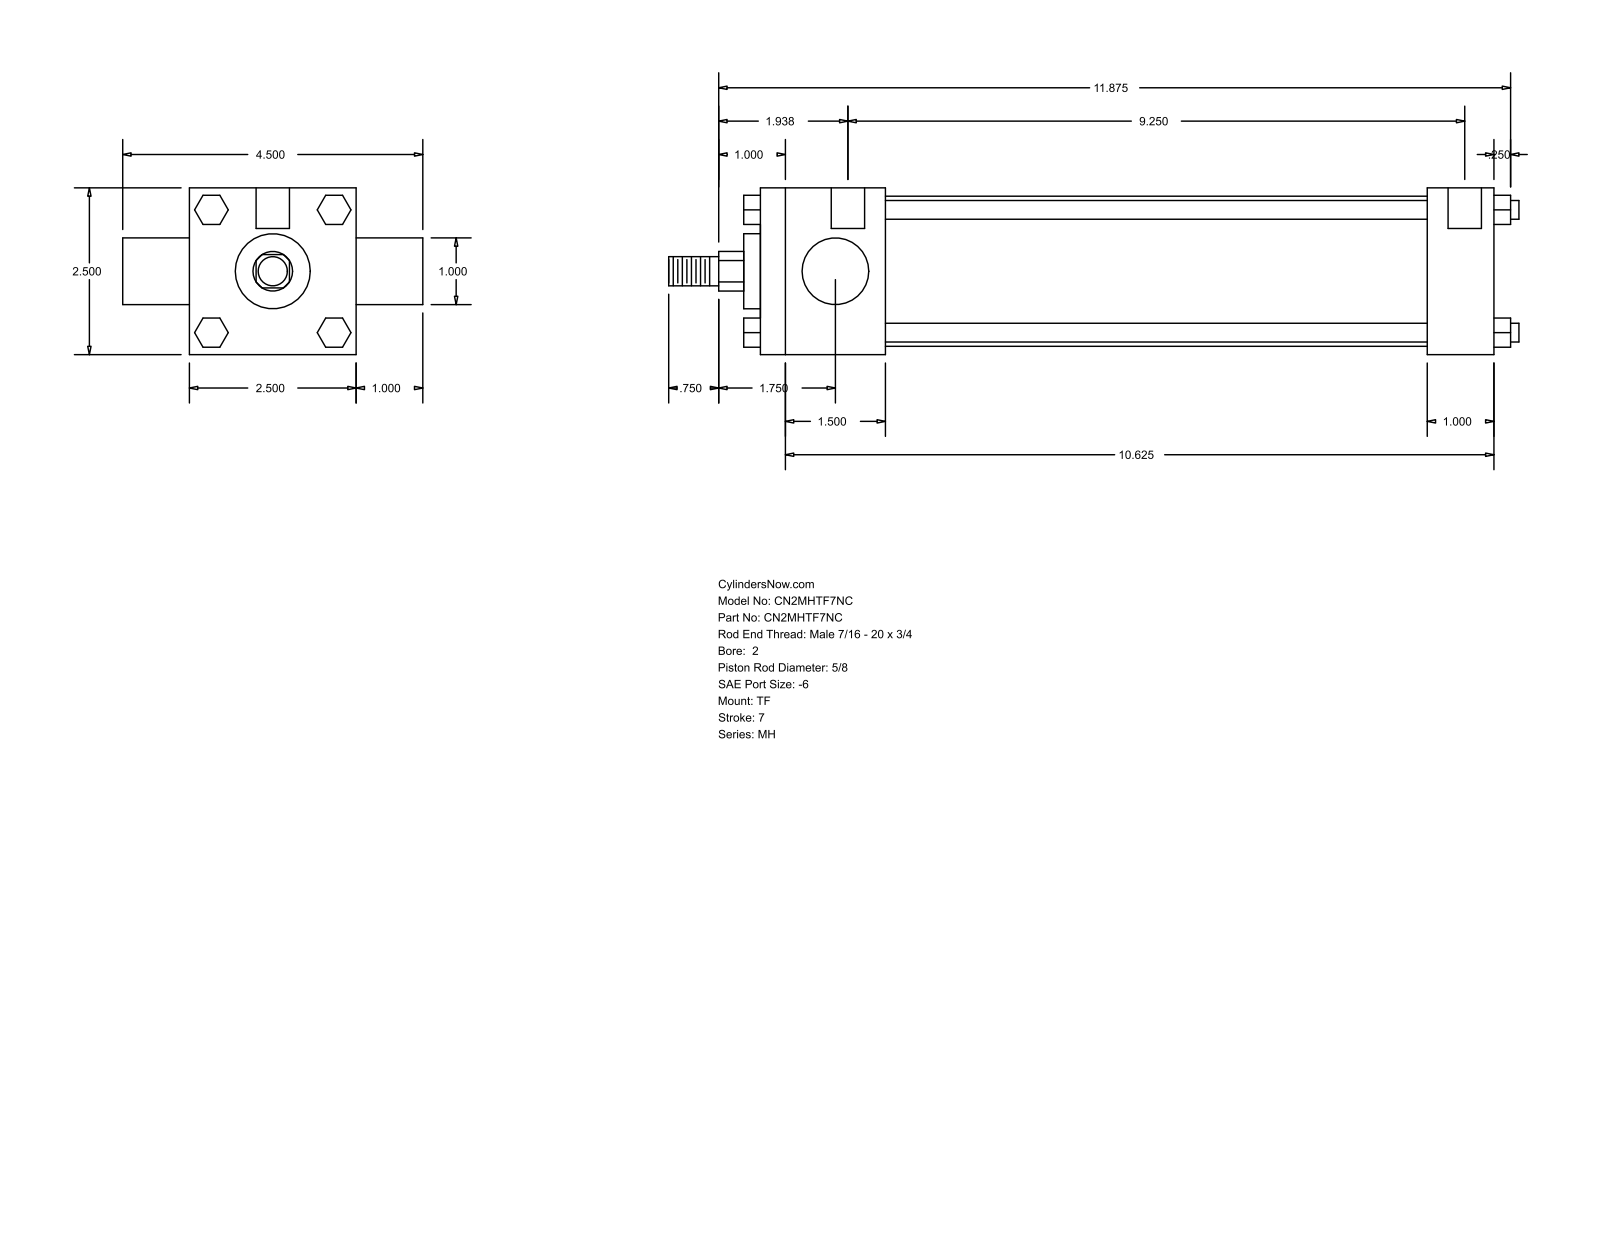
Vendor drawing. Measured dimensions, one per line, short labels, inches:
name: MH_TF__0200_0.625
written by: GSSL Pune (CONFIG_CONTROL_DESIGN)
unit: in
bodies: 0 solids, 120 faces (92 planar, 28 cylindrical, 0 other)
size: 12.75 × 4.5 × 2.5
holes: 3× ⌀0.219, 2× ⌀0.5
bosses: 4× ⌀0.281, 1× ⌀2.25, 1× ⌀1.125, 1× ⌀1, 1× ⌀0.625, 1× ⌀0.437
rounds: 1× R0.297
face distances: 2.5, 11, 1.875, 10, 8.125, 9.125, 1, 1, 0.25, 3.5
hole spacings: 0.125, 0.187, 9.25, 9.375, 9.437, 9.563
